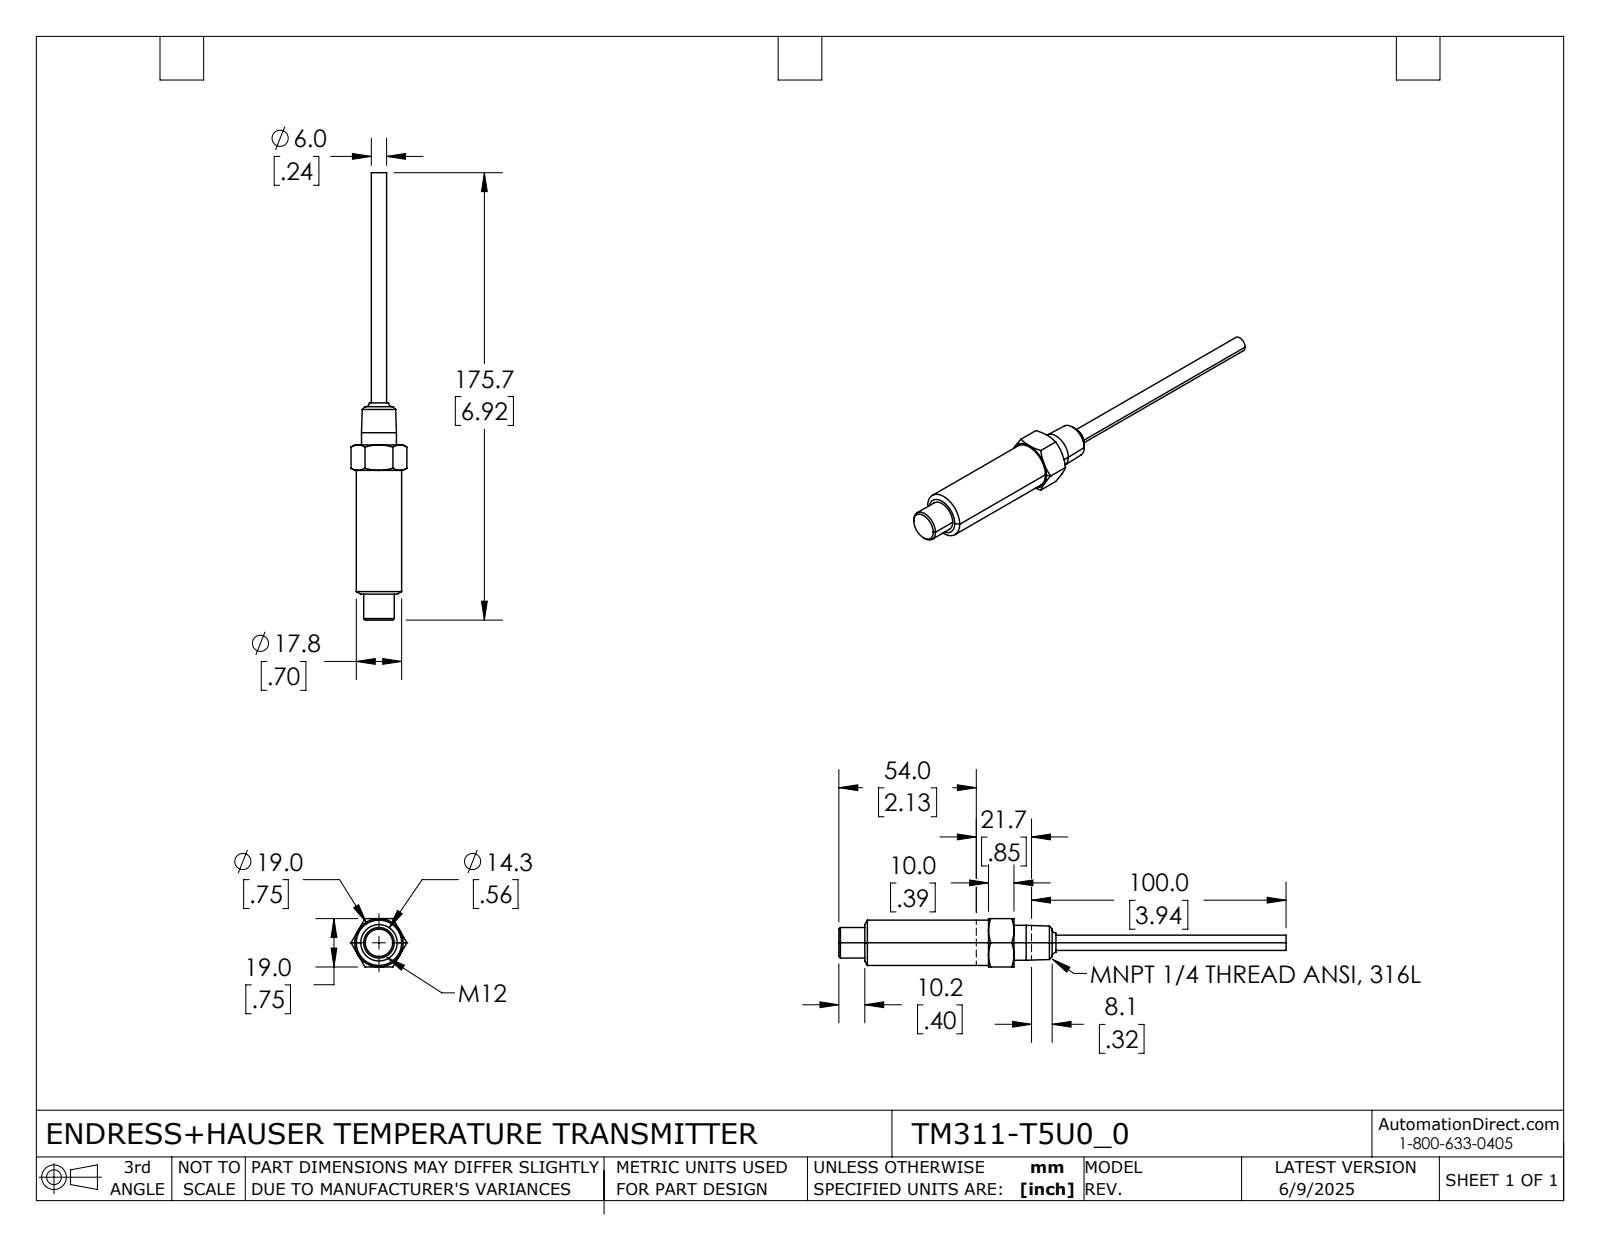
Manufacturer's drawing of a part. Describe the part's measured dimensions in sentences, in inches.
The part is named "TM311-T5U0_0". Its 3-D file was written by "SolidWorks 2021 (AUTOMOTIVE_DESIGN)". It is 1 solid with 47 faces: 13 planar, 8 cylindrical and 26 other. Overall it measures 6.917 by 0.864 by 0.748 inches. Its volume is 1.286 cubic inches and its surface area 10.26 square inches. Round bosses or shafts: 1 of diameter 0.701, 1 of diameter 0.54, 1 of diameter 0.472, 1 of diameter 0.236. The main face-to-face distances are 0.748, 2.709, 2.307, 0.402, 0.394, 1.913, 2.315, 4.209, 4.602, 6.516.
